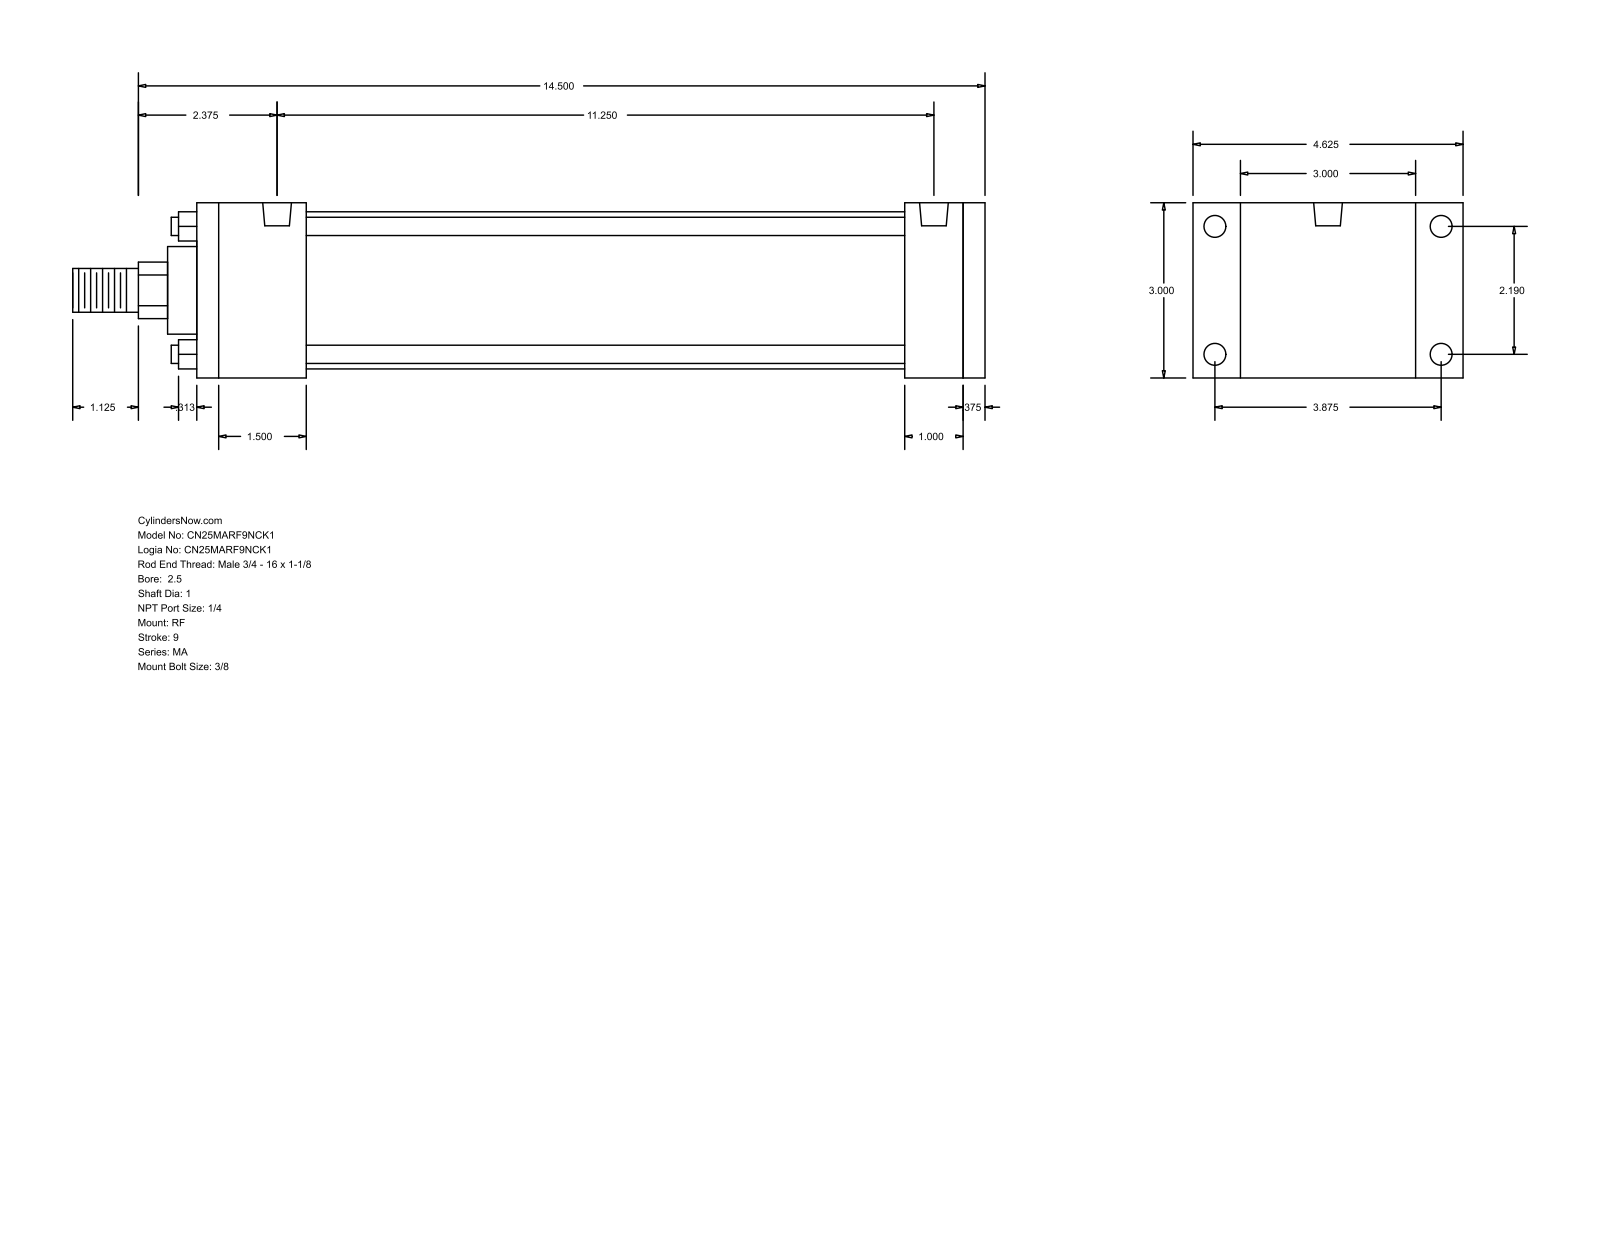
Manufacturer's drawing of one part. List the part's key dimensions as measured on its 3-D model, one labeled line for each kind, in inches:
Part name (STEP PRODUCT): MA_RF__0250_1
STEP written by: GSSL Pune (CONFIG_CONTROL_DESIGN)
Units: inches
Bodies: 0 solids, 92 faces (64 planar, 28 cylindrical, 0 other)
Overall size (bounding box): 15.625 × 4.625 × 3
Round holes (diameter × count): ⌀0.313 ×4, ⌀0.375 ×4, ⌀0.492 ×2
Round bosses / shafts (diameter × count): ⌀0.313 ×4, ⌀2.69 ×1, ⌀1.5 ×1, ⌀1 ×1, ⌀0.75 ×1
Partial cylindrical surfaces — rounded edges, fillets, slot ends (radius × count): R0.484 ×1
Main face-to-face distances: 3, 13.5, 0.375, 13.125, 1.875, 12.125, 10.25, 11.25, 11.625, 1
Hole centre spacings: 2.19, 3.875, 4.451, 11.25
